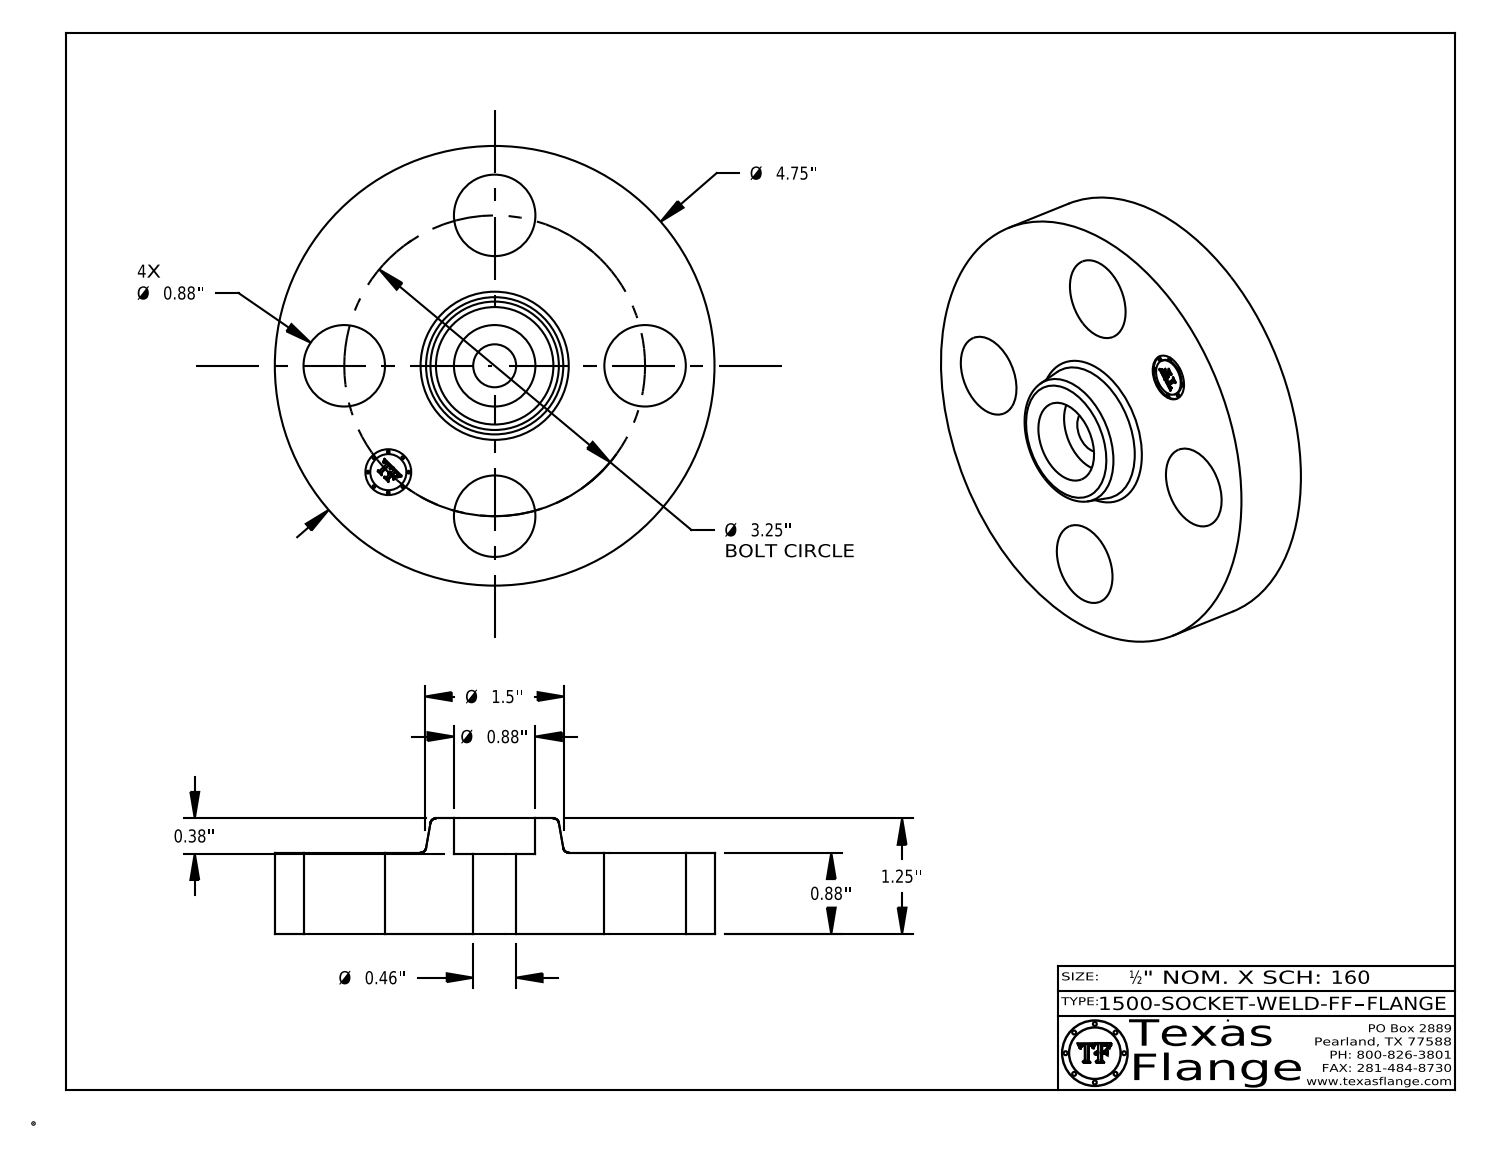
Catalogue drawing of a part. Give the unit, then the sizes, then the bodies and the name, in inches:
Units: inches
Overall size (bounding box): 4.75 × 4.75 × 1.25
Round holes (diameter × count): ⌀0.88 ×5, ⌀0.464 ×1, ⌀0.495 ×1
Round bosses / shafts (diameter × count): ⌀0.03 ×8, ⌀4.75 ×1, ⌀0.39 ×1
Main face-to-face distances: 0.88, 1.25, 0.37, 0.87, 0.38, 0.865, 0.015, 0.385, 0.148, 0.144
Hole centre spacings: 1.625, 2.298, 1.244, 3.003, 3.25
Volume: 13.67 in³ · Surface area: 56.76 in²
Bodies: 1 solid, 409 faces (369 planar, 34 cylindrical, 6 other)
Part name (STEP PRODUCT): 1500-SOCKET-WELD-FF
STEP written by: CATIA V5 STEP AP214 (AUTOMOTIVE_DESIGN)
